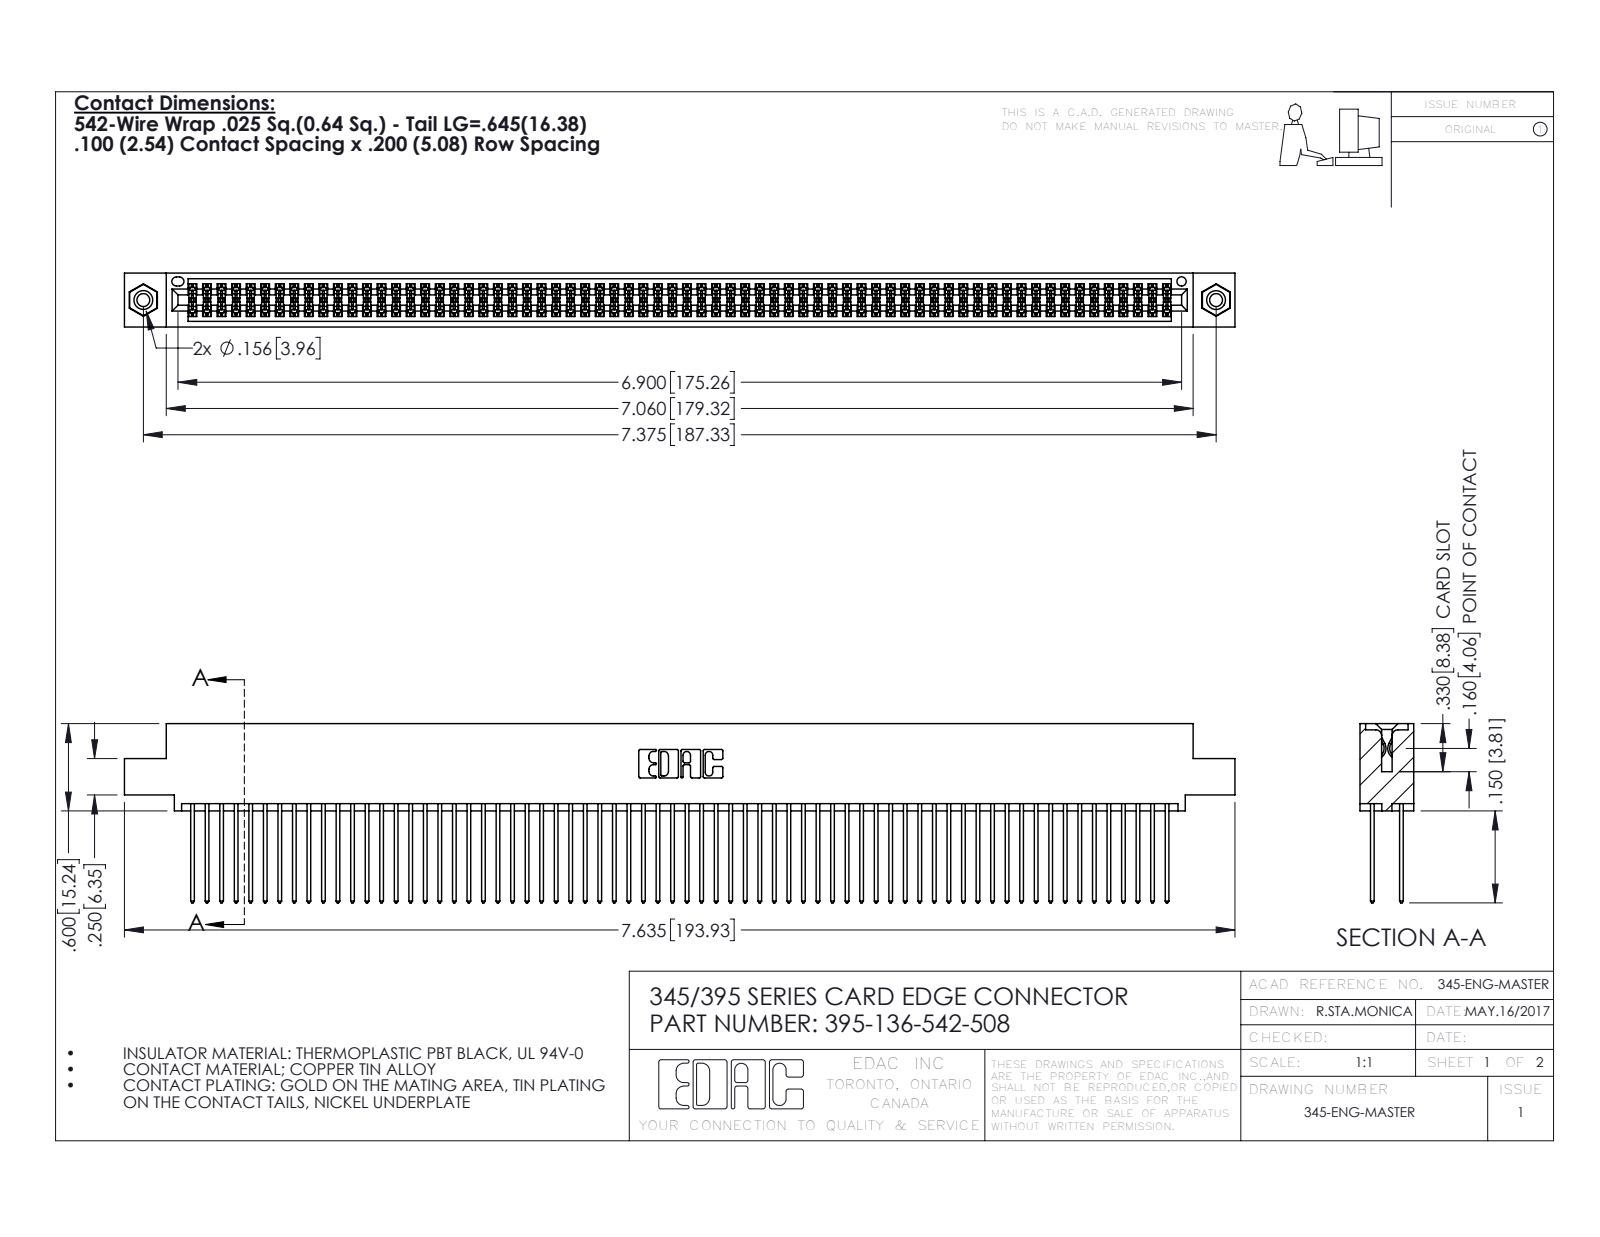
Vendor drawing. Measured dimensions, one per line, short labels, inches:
name: 345 Part_0.110 Offset - 0.156 Dia-TI; 345-250-001_345-250-003-102; 395-136-542-508; 345-292-001_345-293-142
written by: SolidWorks 2016 (CONFIG_CONTROL_DESIGN)
unit: in
bodies: 139 solids, 6990 faces (4604 planar, 2370 cylindrical, 16 other)
size: 7.635 × 1.232 × 0.37
volume: 1.198 in³; area: 50.52 in²
holes: 2× ⌀0.089, 2× ⌀0.125, 2× ⌀0.156, 1× ⌀0.064
bosses: 2× ⌀0.155
rounds: 204× R0.006, 136× R0.01, 22× R0.01, 6× R0.007, 6× R0.031, 3× R0.026, 2× R0.014, 2× R0.019
face distances: 0.072, 0.298, 0.2, 0.098, 0.272, 0.025, 0.225, 0.37, 0.175, 0.149
hole spacings: 0.27, 7.139, 7.375
